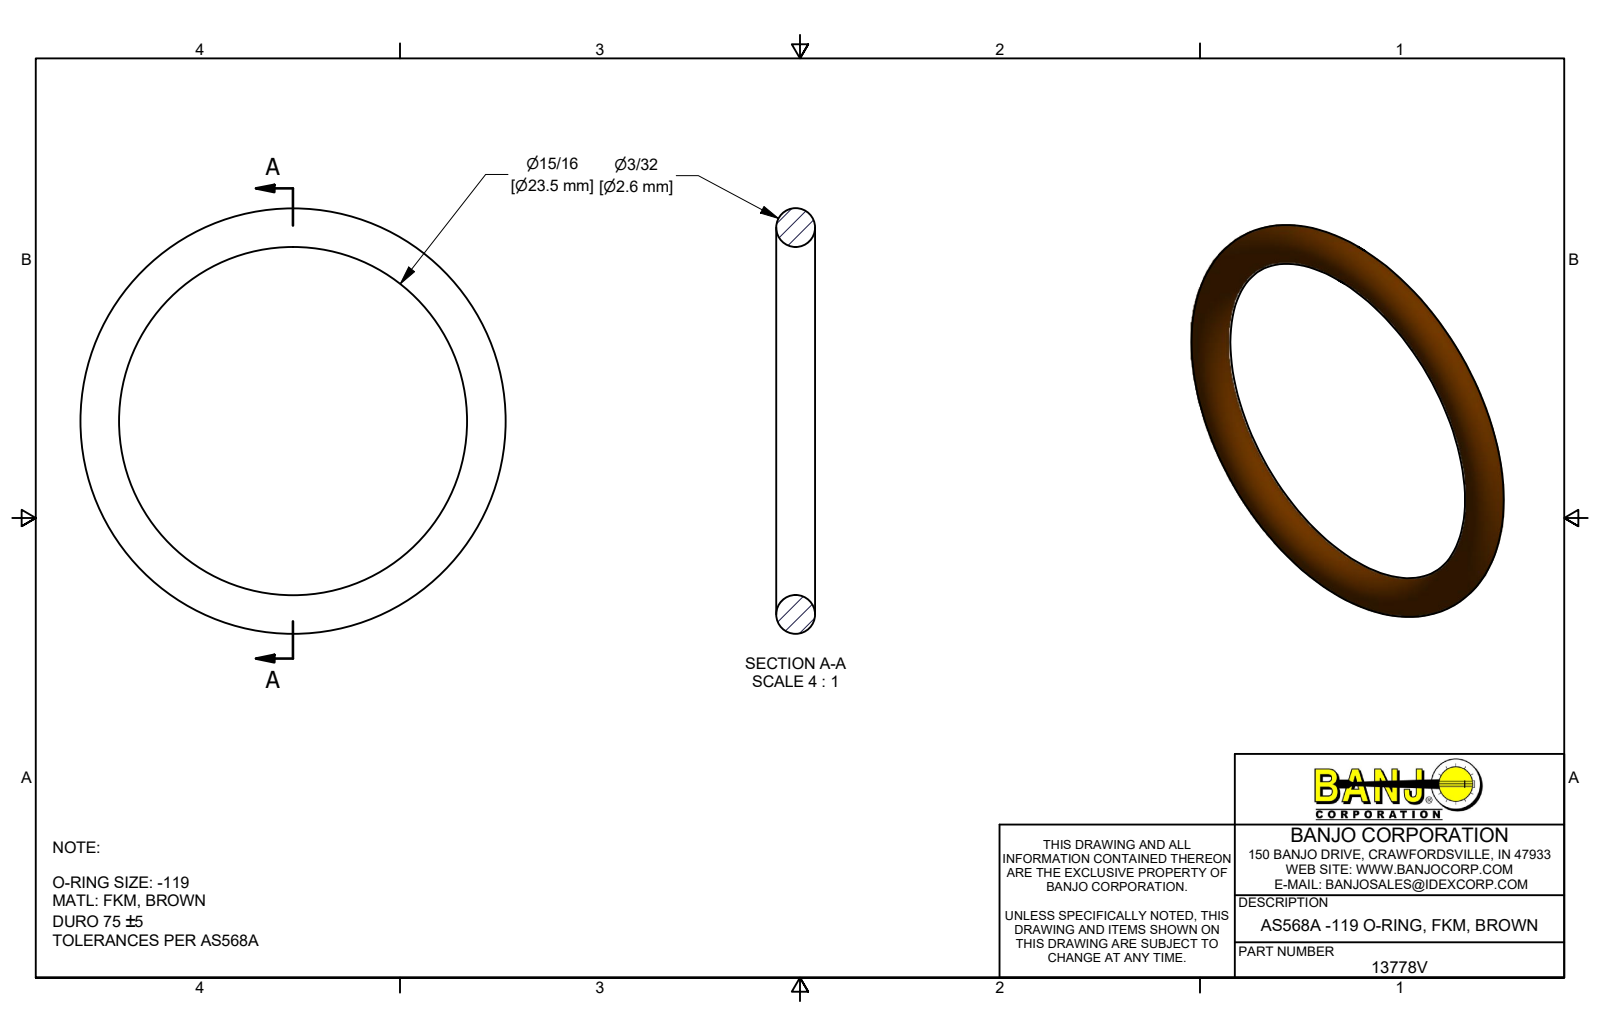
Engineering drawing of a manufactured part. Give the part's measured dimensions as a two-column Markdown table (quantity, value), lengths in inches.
| quantity | value |
| --- | --- |
| part name | 13778V |
| STEP written by | Autodesk Inventor 2019 (AUTOMOTIVE_DESIGN) |
| units | inches |
| bodies | 1 solid, 1 faces (0 planar, 0 cylindrical, 1 other) |
| overall size | 1.13 × 1.13 × 0.103 |
| volume | 0.027 in³ |
| surface area | 1.044 in² |
